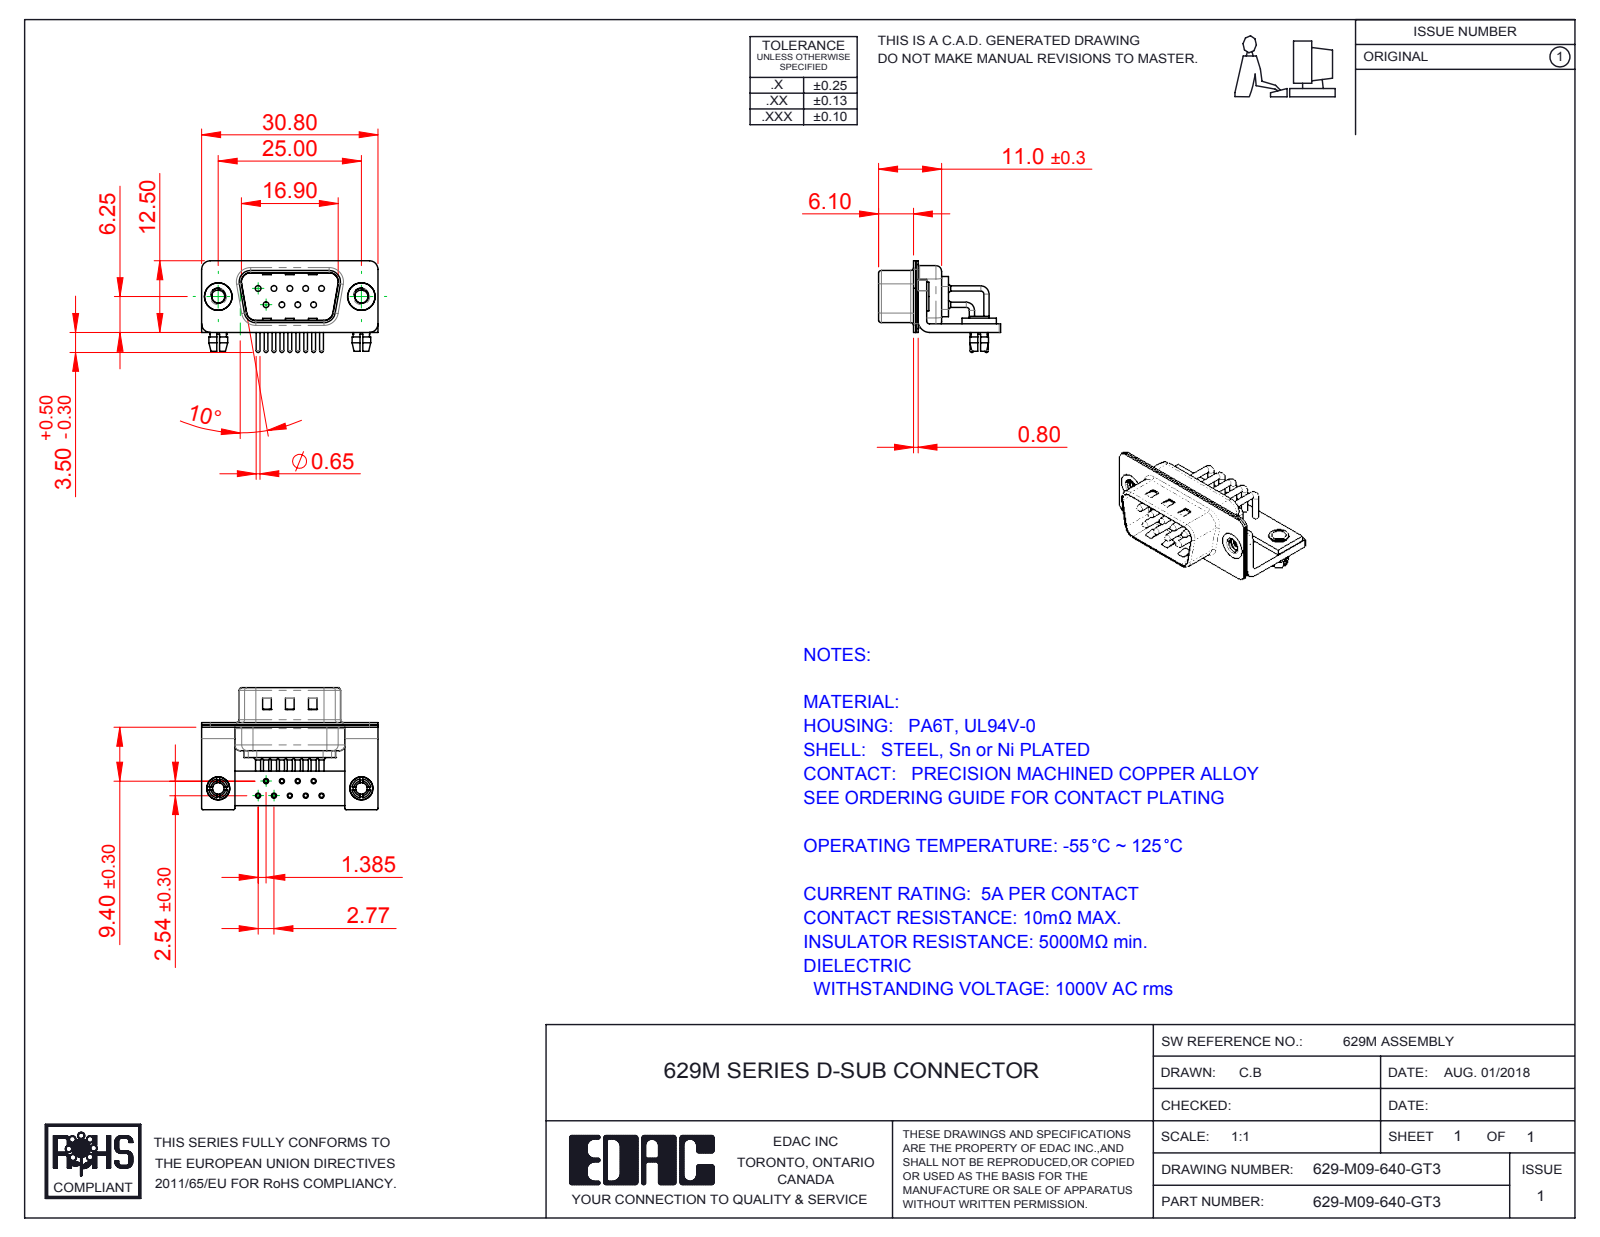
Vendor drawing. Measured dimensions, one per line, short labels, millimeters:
name: 629M Shell Front_09 Contacts; 629M Shell Rear_09 Contacts; 629M Contact Row 1; 629M Housing_09 Contacts (+6 more)
written by: SolidWorks 2016 (CONFIG_CONTROL_DESIGN)
unit: mm
bodies: 19 solids, 1454 faces (757 planar, 525 cylindrical, 172 other)
size: 30.8 × 21.3 × 16
volume: 1 856 mm³; area: 5 184 mm²
holes: 11× ⌀2, 9× ⌀0.9, 9× ⌀1, 9× ⌀1.7, 2× ⌀2.26, 2× ⌀2.5, 2× ⌀3.2, 2× ⌀4, 2× ⌀4.8
bosses: 9× ⌀1.5, 9× ⌀0.9, 9× ⌀0.65, 2× ⌀5, 2× ⌀4.9, 2× ⌀4, 2× ⌀3.4, 2× ⌀3.3
rounds: 16× R0.25, 16× R1.5, 13× R2, 9× R0.5, 9× R1.01, 8× R1.6, 4× R0.6, 4× R0.65
face distances: 0.4, 1.5, 0.8, 0.85, 1.25, 1.9, 1, 2.5, 10.4, 9.55
hole spacings: 2.77, 5.54, 3.16, 4.87, 8.31, 2.89, 2.9, 5.03
